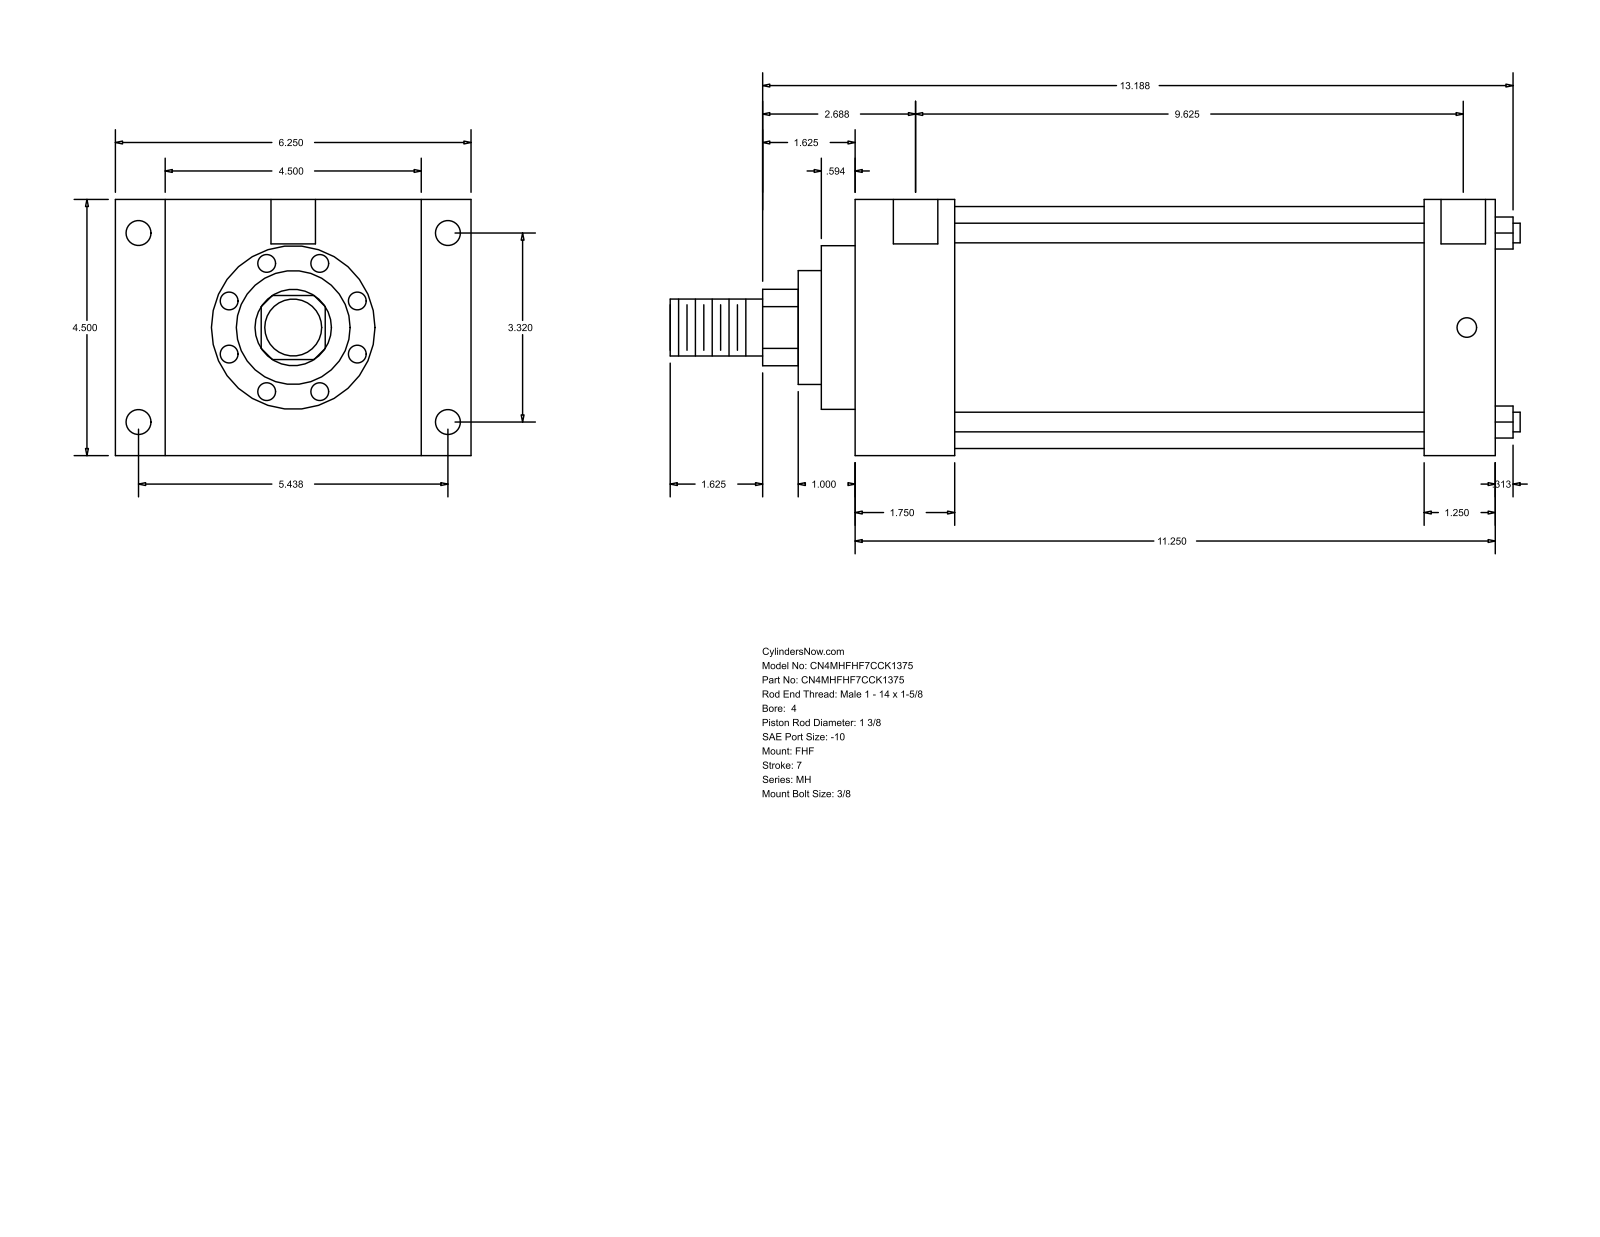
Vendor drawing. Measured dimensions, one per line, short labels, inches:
name: MH_FHF__0400_1.375
written by: GSSL Pune (CONFIG_CONTROL_DESIGN)
unit: in
bodies: 0 solids, 90 faces (61 planar, 29 cylindrical, 0 other)
size: 14.937 × 6.25 × 4.5
holes: 4× ⌀0.344, 4× ⌀0.438, 2× ⌀0.781
bosses: 4× ⌀0.345, 1× ⌀4.25, 1× ⌀2.875, 1× ⌀2, 1× ⌀1.375, 1× ⌀1
rounds: 1× R0.672
face distances: 4.5, 11.25, 1.75, 9.5, 0.875, 5.375, 6.25, 10, 8.25, 1.25
hole spacings: 3.32, 5.438, 6.371, 9.75, 0.062, 0.063, 9.625, 9.687
